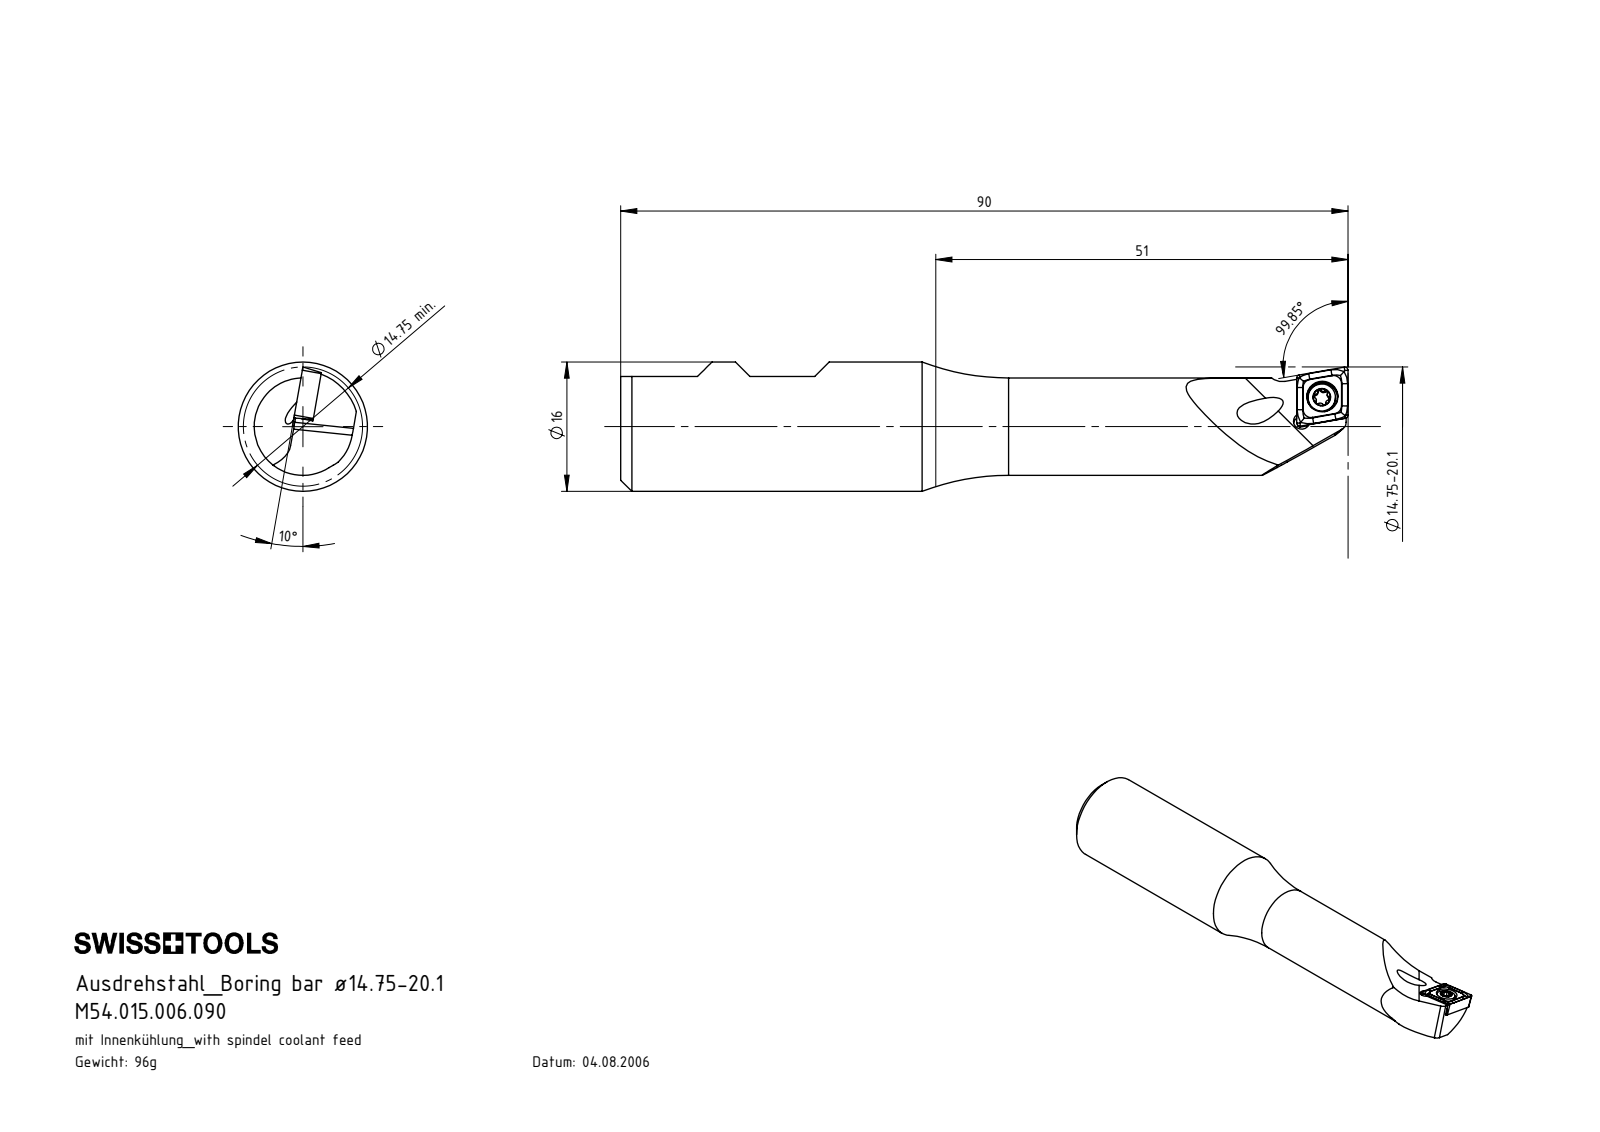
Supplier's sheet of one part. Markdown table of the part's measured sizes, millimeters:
| quantity | value |
| --- | --- |
| part name | WCA-ER2.001.006_A; CCMT060204; B15-WCA.K11.090_A; B15.WCA.K11.090 |
| STEP written by | SolidWorks 2017 (AUTOMOTIVE_DESIGN) |
| units | millimeters |
| bodies | 3 solids, 100 faces (33 planar, 26 cylindrical, 41 other) |
| overall size | 90 × 16 × 16 |
| volume | 12 162 mm³ |
| surface area | 4 986 mm² |
| round holes (diameter × count) | 3 × 2, 2 × 1, 2.05 × 1, 2.8 × 1, 3.85 × 1 |
| round bosses / shafts (diameter × count) | 16 × 1, 12.05 × 1, 3.4 × 1, 2.5 × 1 |
| partial cylindrical surfaces (radius × count) | 0.21 × 6, 0.36 × 5, 0.36 × 1, 1 × 1, 6.2 × 1, 7 × 1, 8 × 1 |
| main face-to-face distances | 2.18, 10.25, 5.1, 7.28, 7.48, 2.38, 83.76, 1.48, 6.58, 0.7 |
| hole center spacings | 3.89, 3.99 |
